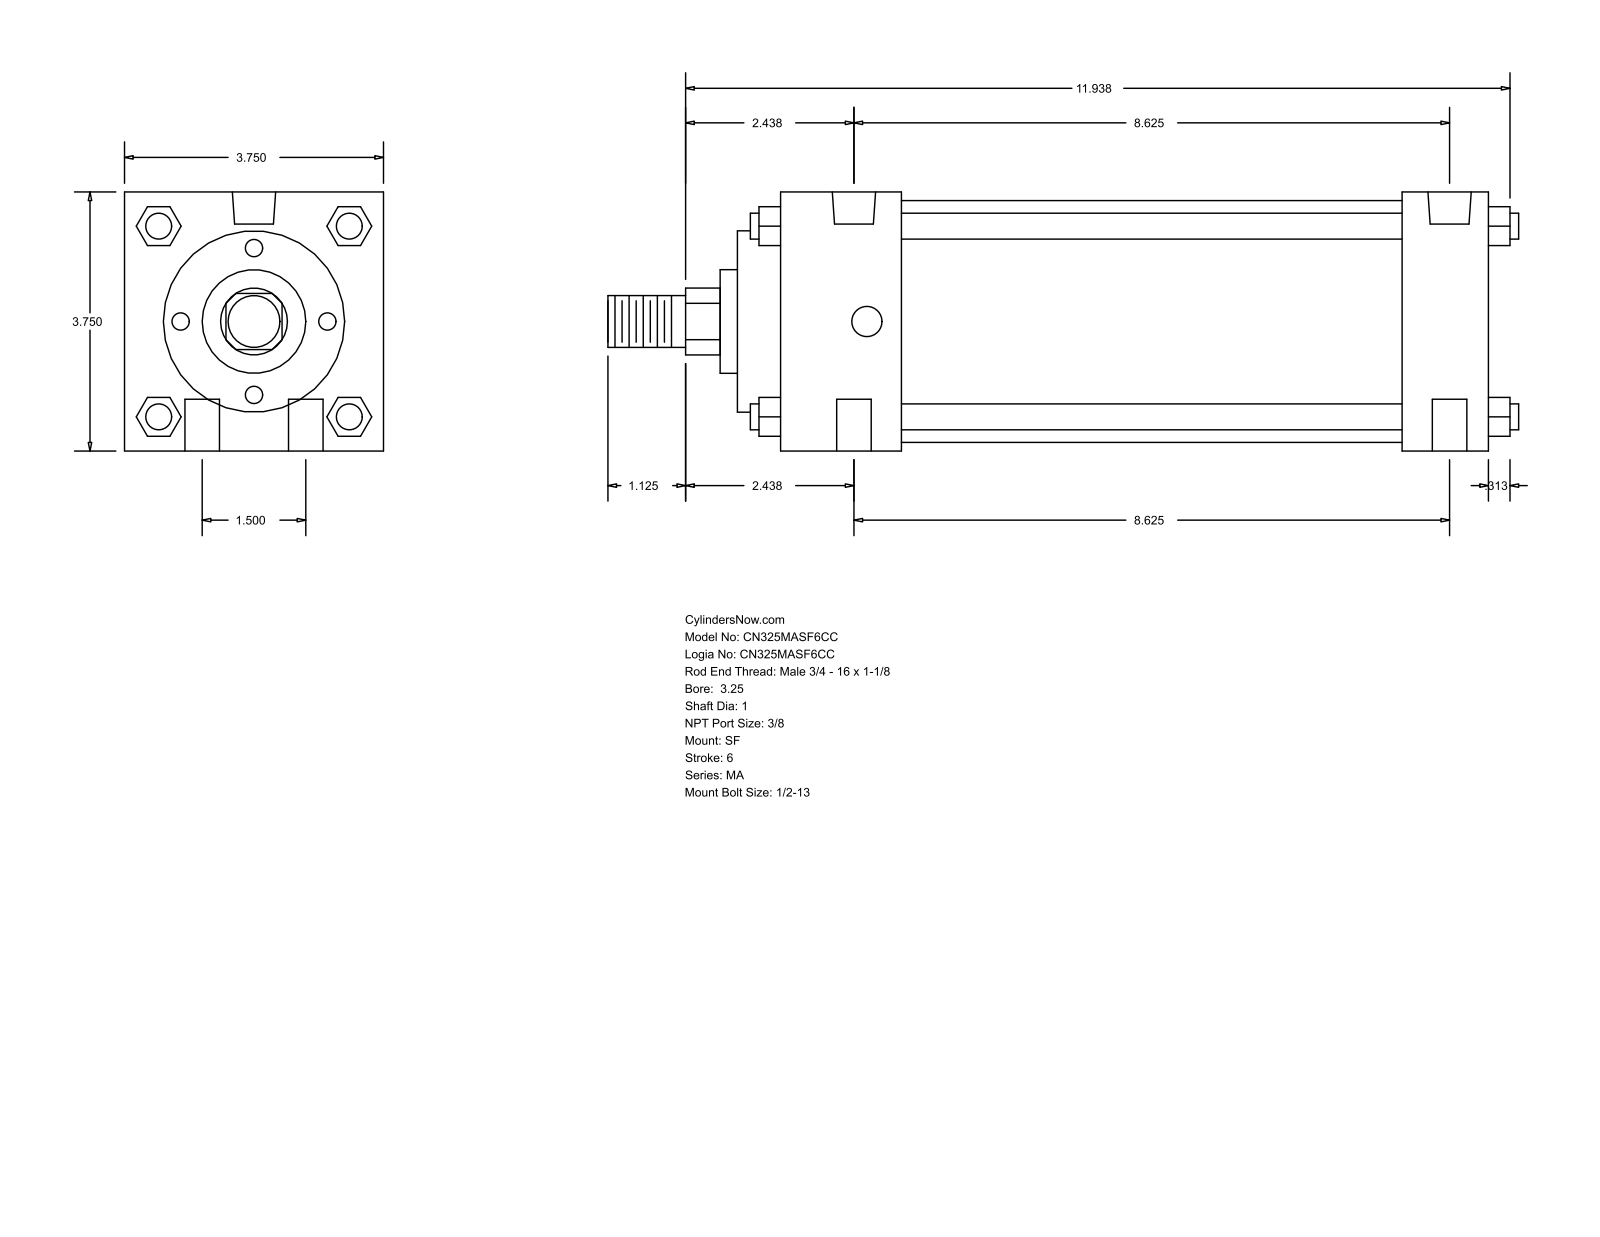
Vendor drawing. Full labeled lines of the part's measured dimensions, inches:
Part name (STEP PRODUCT): MA_SF__0325_1
STEP written by: GSSL Pune (CONFIG_CONTROL_DESIGN)
Units: inches
Bodies: 0 solids, 126 faces (95 planar, 31 cylindrical, 0 other)
Overall size (bounding box): 13.187 × 3.75 × 3.75
Round holes (diameter × count): ⌀0.5 ×4, ⌀0.437 ×2, ⌀0.627 ×2
Round bosses / shafts (diameter × count): ⌀0.375 ×4, ⌀3.5 ×1, ⌀2.625 ×1, ⌀1.5 ×1, ⌀1 ×1, ⌀0.75 ×1
Partial cylindrical surfaces — rounded edges, fillets, slot ends (radius × count): R0.484 ×1
Main face-to-face distances: 3.75, 10.25, 10.875, 9, 1.25, 1.75, 7.25, 8.5, 0.625, 2.375
Hole centre spacings: 0.75, 8.658, 8.625, 1.5, 8.755, 8.25
